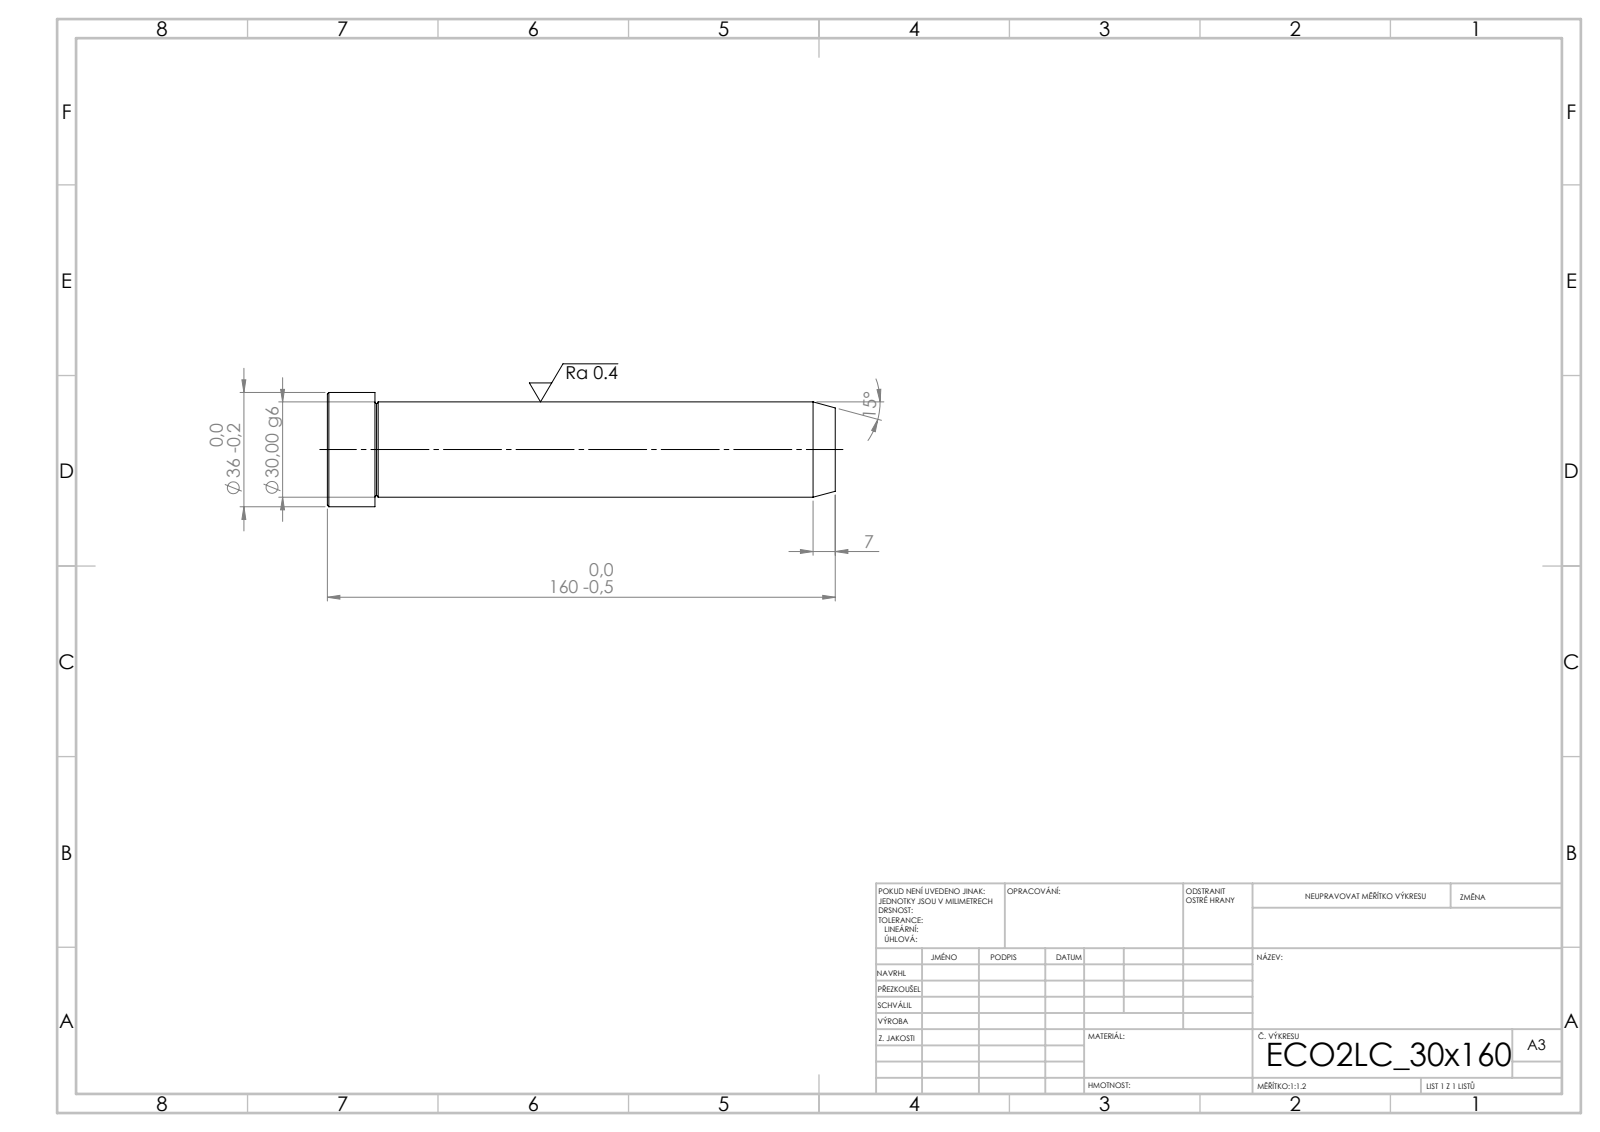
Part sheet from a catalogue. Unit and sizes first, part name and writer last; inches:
Units: inches
Overall size (bounding box): 6.299 × 1.417 × 1.417
Round bosses / shafts (diameter × count): ⌀1.417 ×1, ⌀1.181 ×1
Main face-to-face distances: 6.299, 5.709, 0.591
Volume: 7.147 in³ · Surface area: 26.71 in²
Bodies: 1 solid, 15 faces (3 planar, 4 cylindrical, 8 other)
STEP written by: SolidWorks 2019 (CONFIG_CONTROL_DESIGN)
